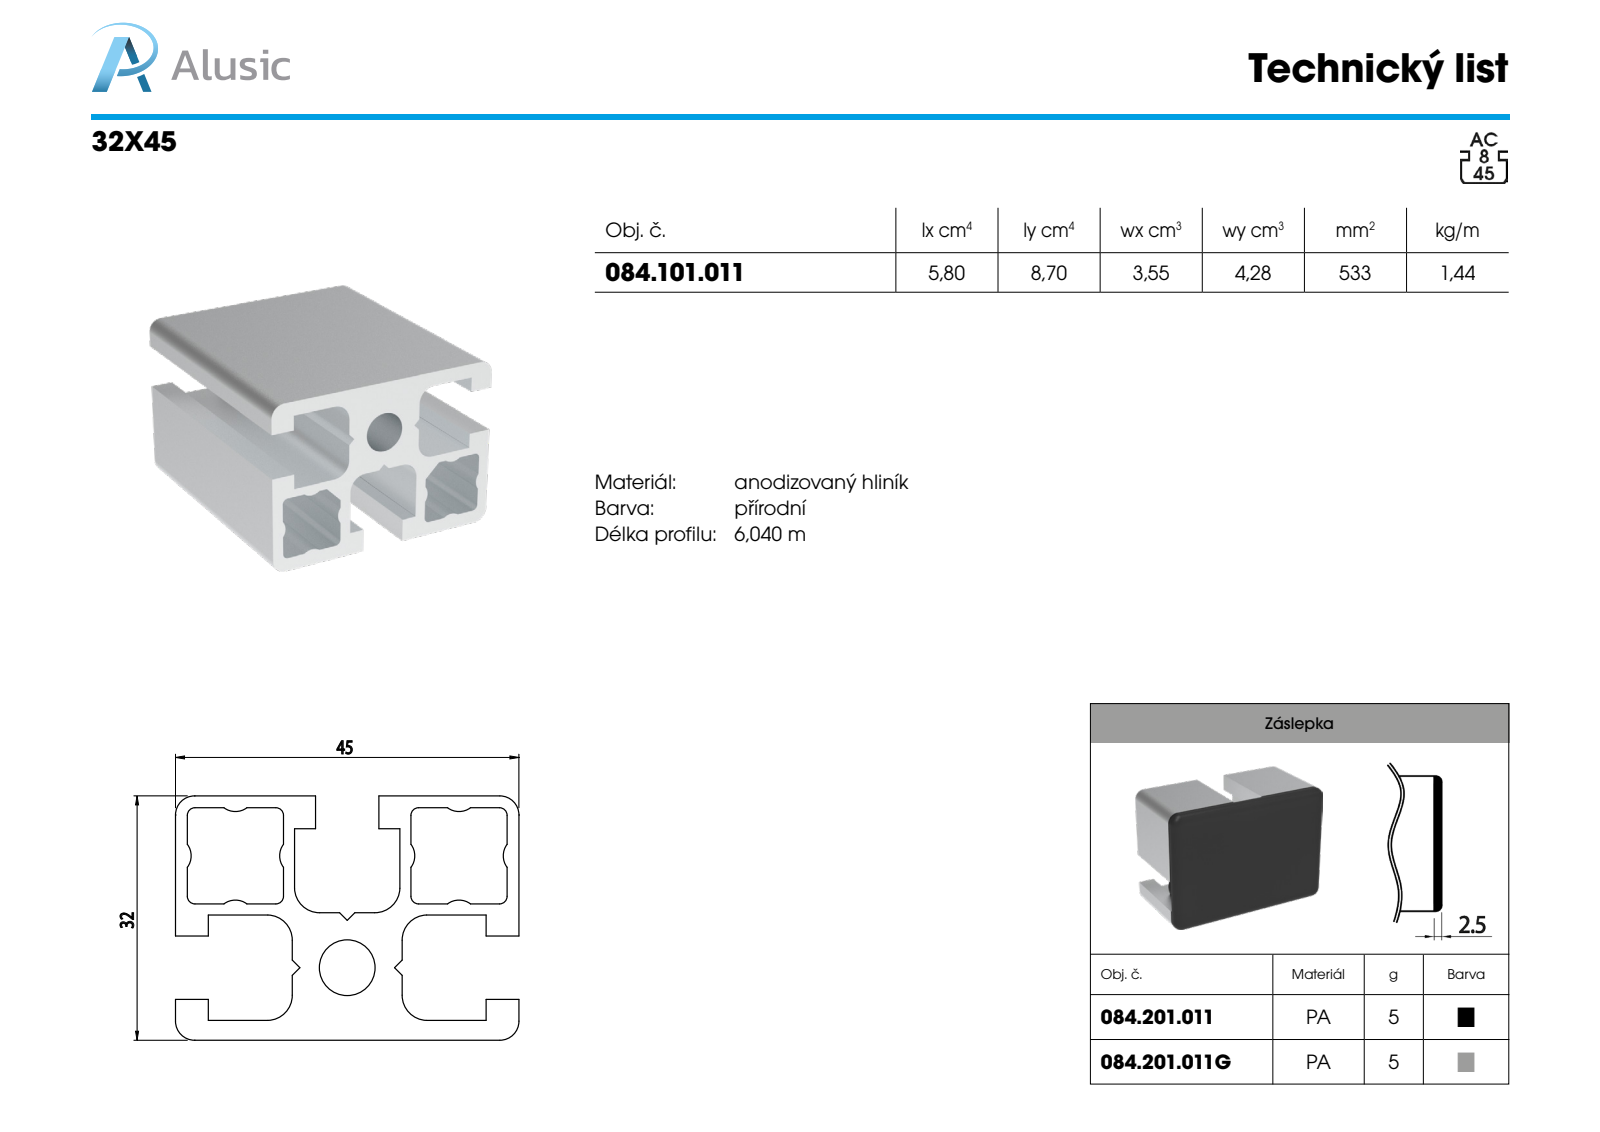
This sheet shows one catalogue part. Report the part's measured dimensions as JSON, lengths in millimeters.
{"part_name": "084.101.011", "step_written_by": "SolidWorks 2018 (AUTOMOTIVE_DESIGN)", "units": "millimeters", "bodies": {"solids": 1, "faces": 85, "planar": 57, "cylindrical": 28, "other": 0}, "overall_size": [100, 45, 32], "volume_mm3": 58706, "surface_area_mm2": 39263, "round_holes": [[7.3, 1]], "partial_cylinders_radius": [[2.5, 12], [1, 6], [3, 6]], "face_to_face_distances": [29.4, 15.6, 32, 14.1, 15.3, 2.75, 11.05, 13.8, 2, 13.6]}
